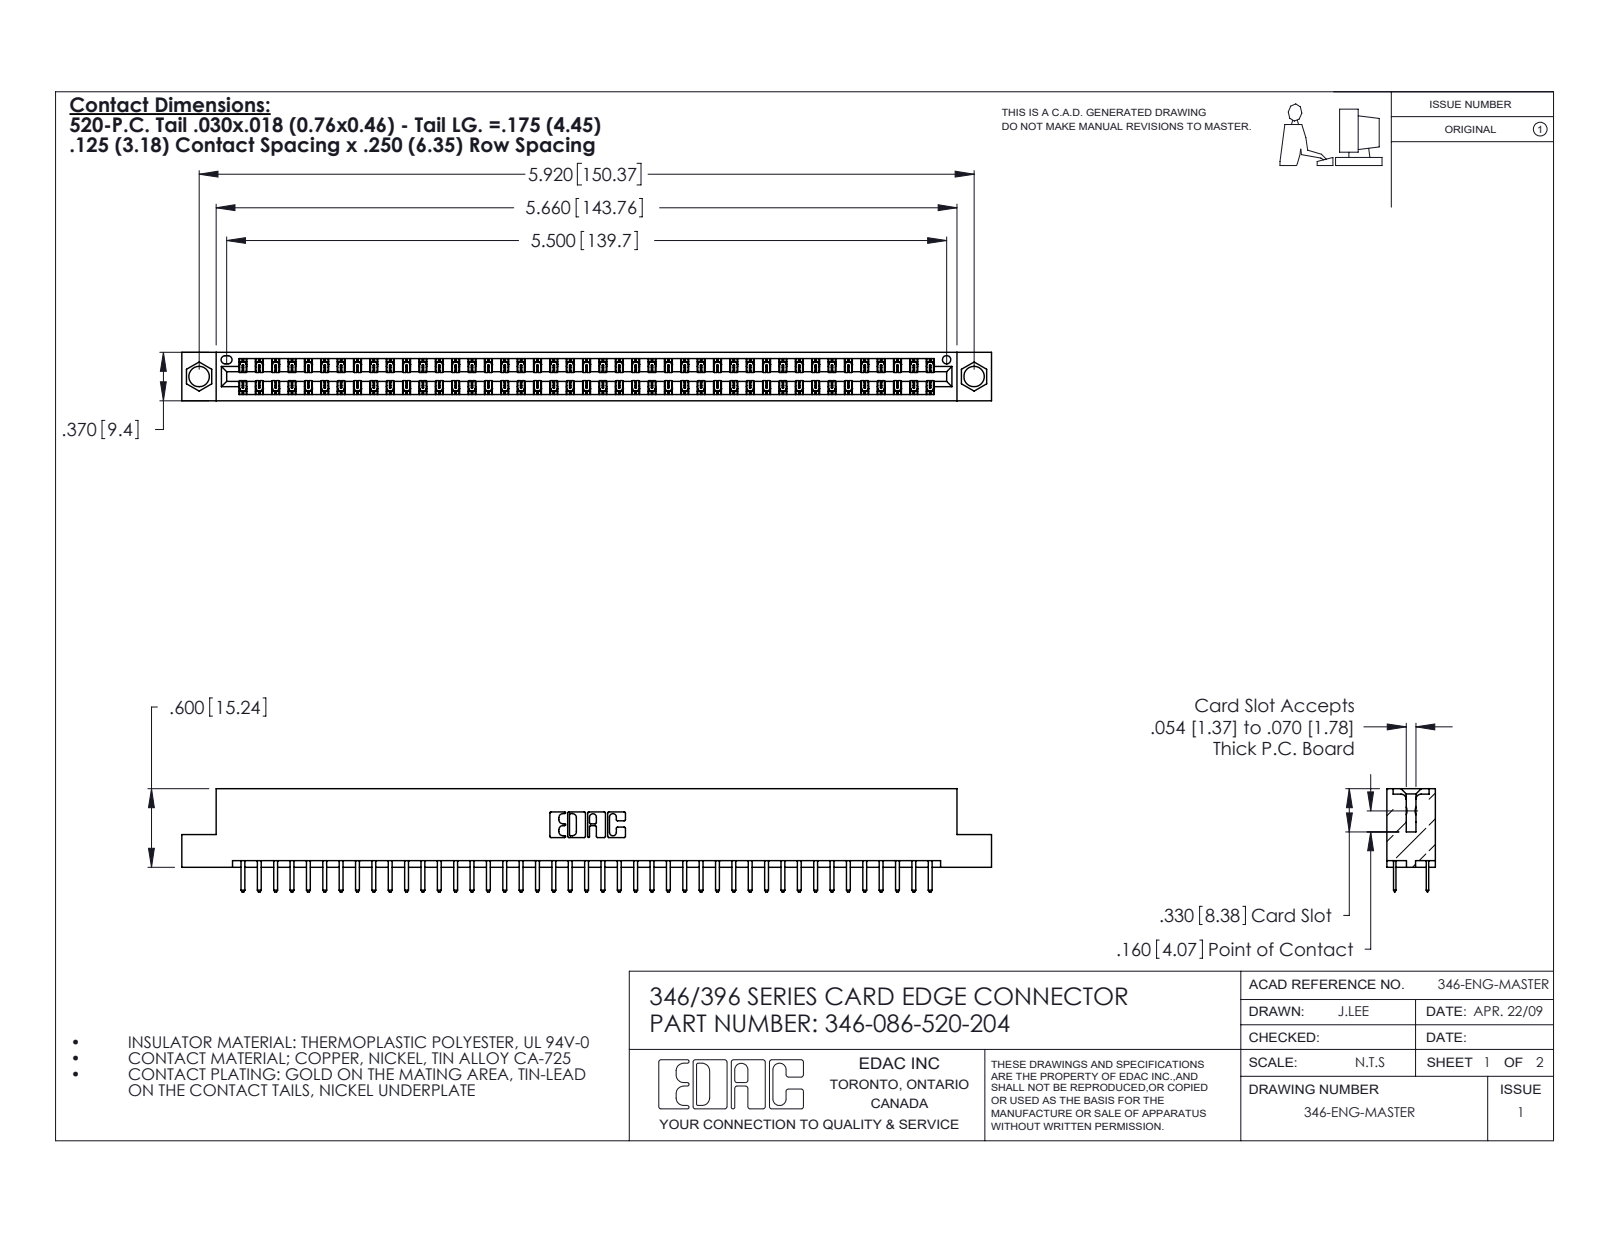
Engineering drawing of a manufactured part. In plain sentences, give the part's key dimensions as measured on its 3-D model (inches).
The part is named "346-086-520-204; 346 Part_Flush Mounting Lugs - 0.156 Dia-TH; 345-292-001_345-293-120". Its 3-D file was written by "SolidWorks 2020 (CONFIG_CONTROL_DESIGN)". It is 87 solids with 4952 faces: 3272 planar, 1680 cylindrical and 0 other. Overall it measures 6.185 by 0.788 by 0.37 inches. Its volume is 0.927 cubic inches and its surface area 32 square inches. Round holes: 2 of diameter 0.156, 1 of diameter 0.064. Partial cylindrical surfaces (rounded edges, fillets, slot ends): 129 of radius 0.006, 90 of radius 0.01, 22 of radius 0.01, 6 of radius 0.007, 6 of radius 0.031, 3 of radius 0.026, 2 of radius 0.014, 2 of radius 0.022. The main face-to-face distances are 0.048, 0.322, 0.25, 0.37, 0.275, 0.072, 0.298, 0.025, 0.148, 0.222. The hole center spacings are 0.246, 5.711, 5.92.
